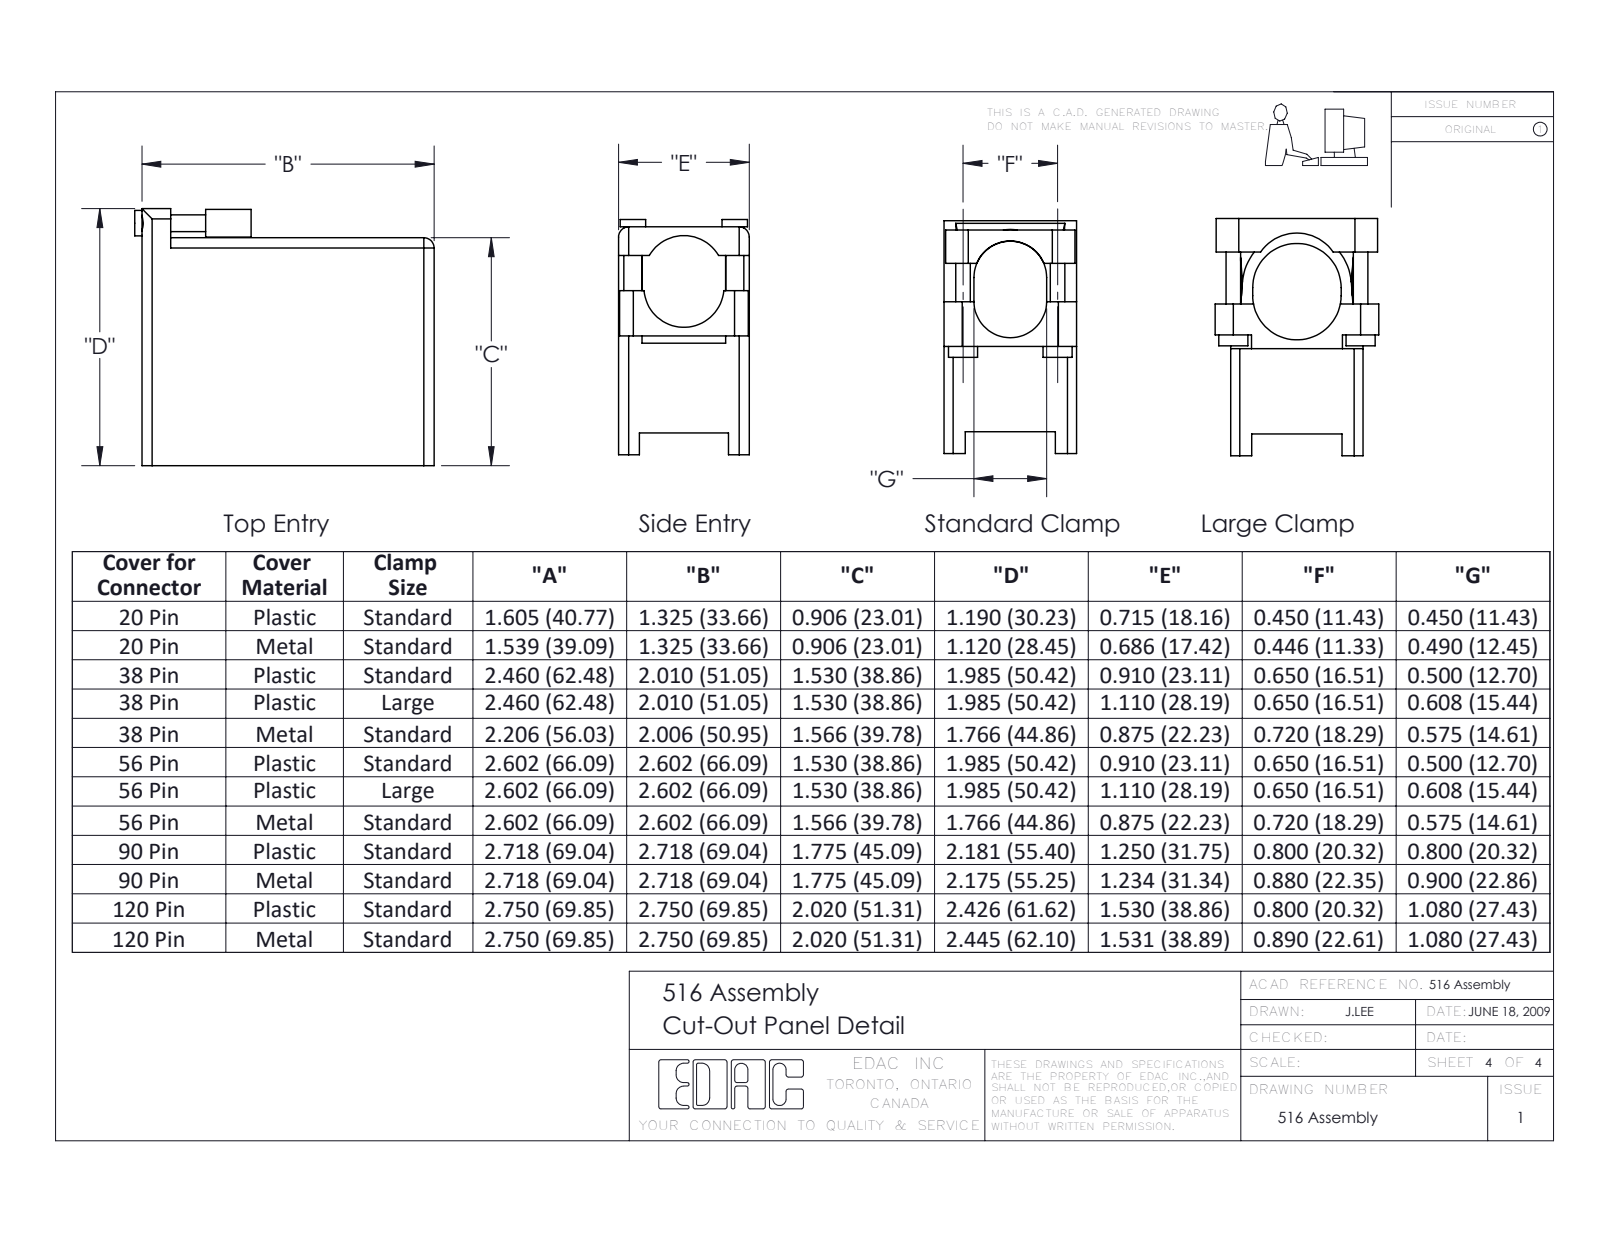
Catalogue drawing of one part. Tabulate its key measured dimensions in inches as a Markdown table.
| quantity | value |
| --- | --- |
| part name | 516-056-501-412; 516-252-035-100_516-252-035-100; 516-221-038-102_056; 516-292-001_501 Contact (+4 more) |
| STEP written by | SolidWorks 2020 (CONFIG_CONTROL_DESIGN) |
| units | inches |
| bodies | 63 solids, 5589 faces (3284 planar, 1886 cylindrical, 419 other) |
| overall size | 2.683 × 2.461 × 0.91 |
| volume | 1.794 in³ |
| surface area | 75.39 in² |
| round holes (diameter × count) | 0.13 × 57, 0.05 × 10, 0.187 × 4, 0.089 × 2, 0.12 × 2, 0.125 × 2, 0.125 × 2, 0.133 × 2, 0.101 × 1, 0.163 × 1, 0.203 × 1, 0.208 × 1 |
| round bosses / shafts (diameter × count) | 0.25 × 2, 0.2 × 2, 0.112 × 2, 0.1 × 2, 0.08 × 2 |
| partial cylindrical surfaces (radius × count) | 0.022 × 130, 0.008 × 112, 0.016 × 112, 0.012 × 36, 0.01 × 22, 0.007 × 18, 0.02 × 18, 0.08 × 18 |
| main face-to-face distances | 0.05, 0.86, 0.91, 0.81, 0.13, 0.26, 0.017, 0.843, 0.15, 1.19 |
| hole center spacings | 0.15, 0.397, 0.26, 0.3, 0.397, 0.3, 0.541, 0.26 |
